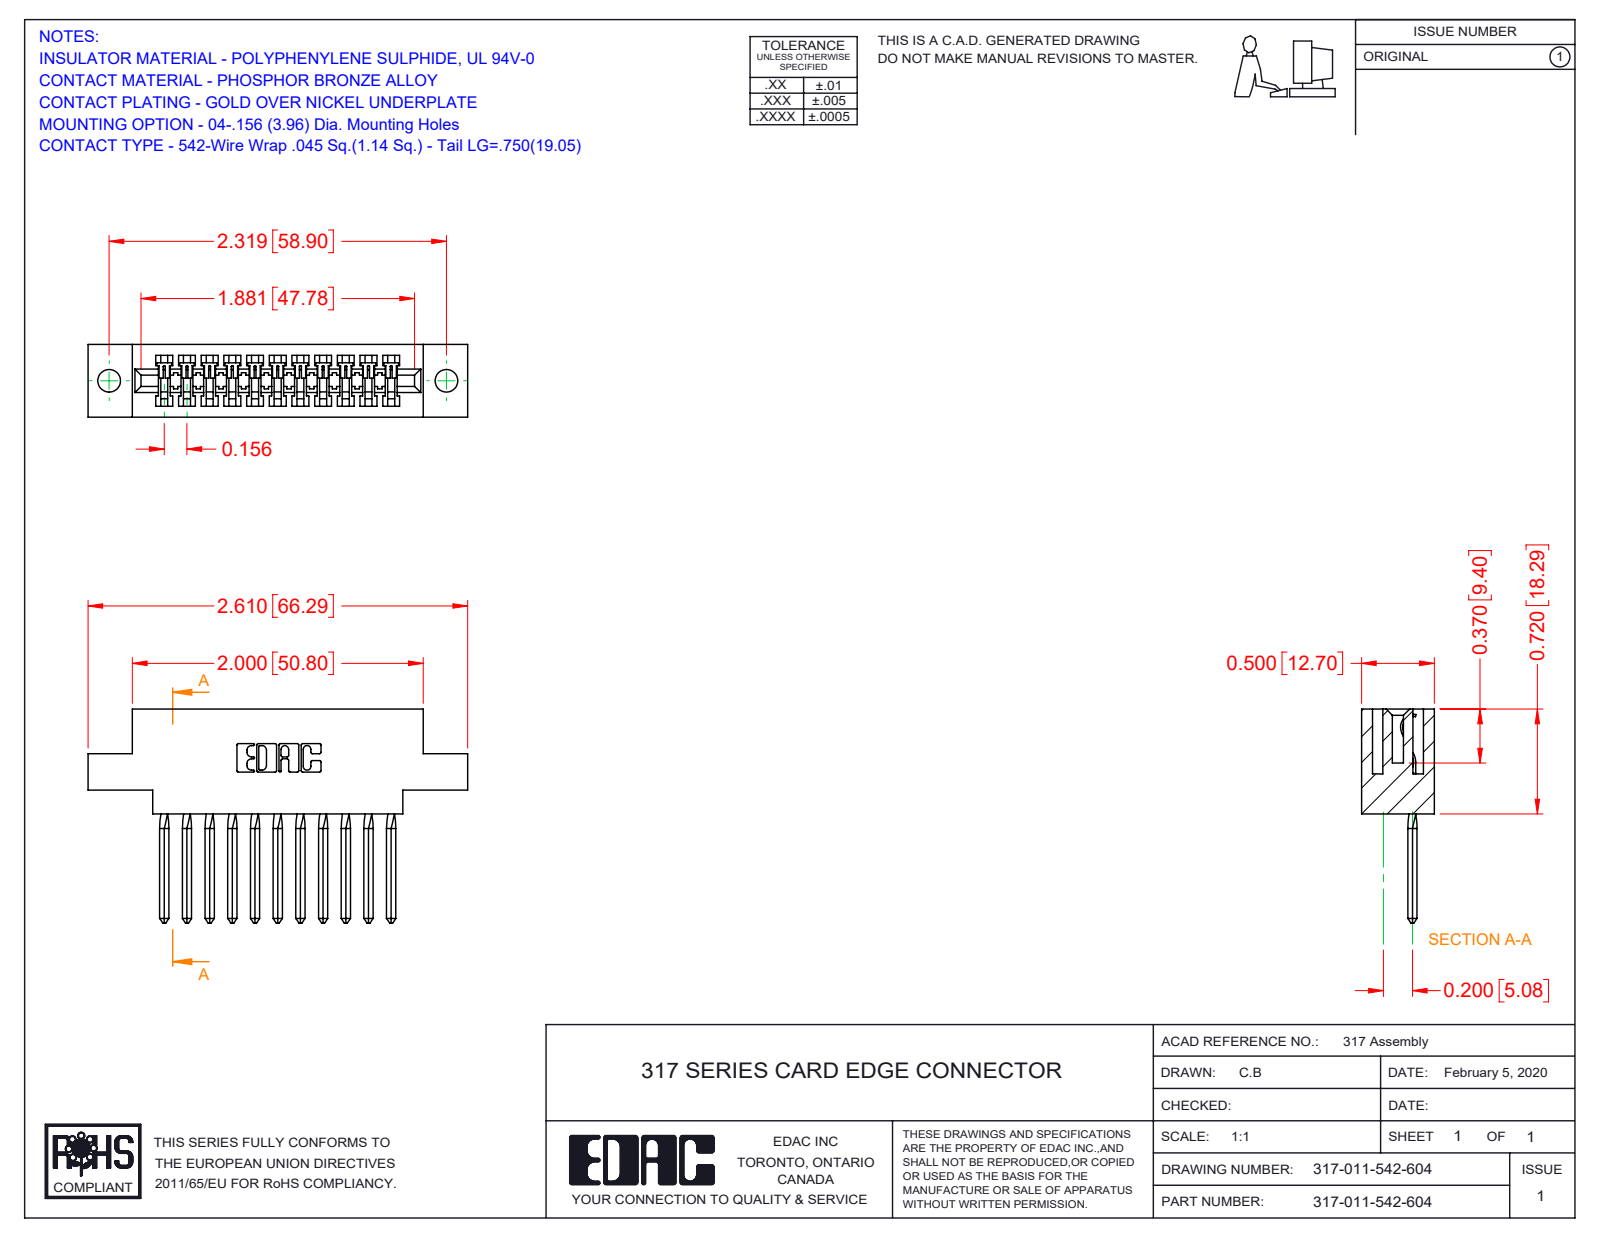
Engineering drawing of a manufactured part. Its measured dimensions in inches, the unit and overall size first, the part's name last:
Units: inches
Overall size (bounding box): 2.61 × 1.47 × 0.5
Round holes (diameter × count): ⌀0.156 ×2
Partial cylindrical surfaces — rounded edges, fillets, slot ends (radius × count): R0.006 ×22, R0.01 ×22, R0.007 ×6, R0.031 ×6, R0.026 ×3, R0.074 ×1, R0.089 ×1, R0.1 ×1
Main face-to-face distances: 0.5, 0.075, 0.425, 0.11, 0.065, 0.22, 0.35, 0.116, 0.136, 0.331
Hole centre spacings: 2.319
Volume: 0.569 in³ · Surface area: 16.26 in²
Bodies: 12 solids, 927 faces (762 planar, 121 cylindrical, 44 other)
Part name (STEP PRODUCT): 317-011-542-604; 317 Part_.156 Dia - TH; 317-290-003_542
STEP written by: SolidWorks 2016 (CONFIG_CONTROL_DESIGN)
